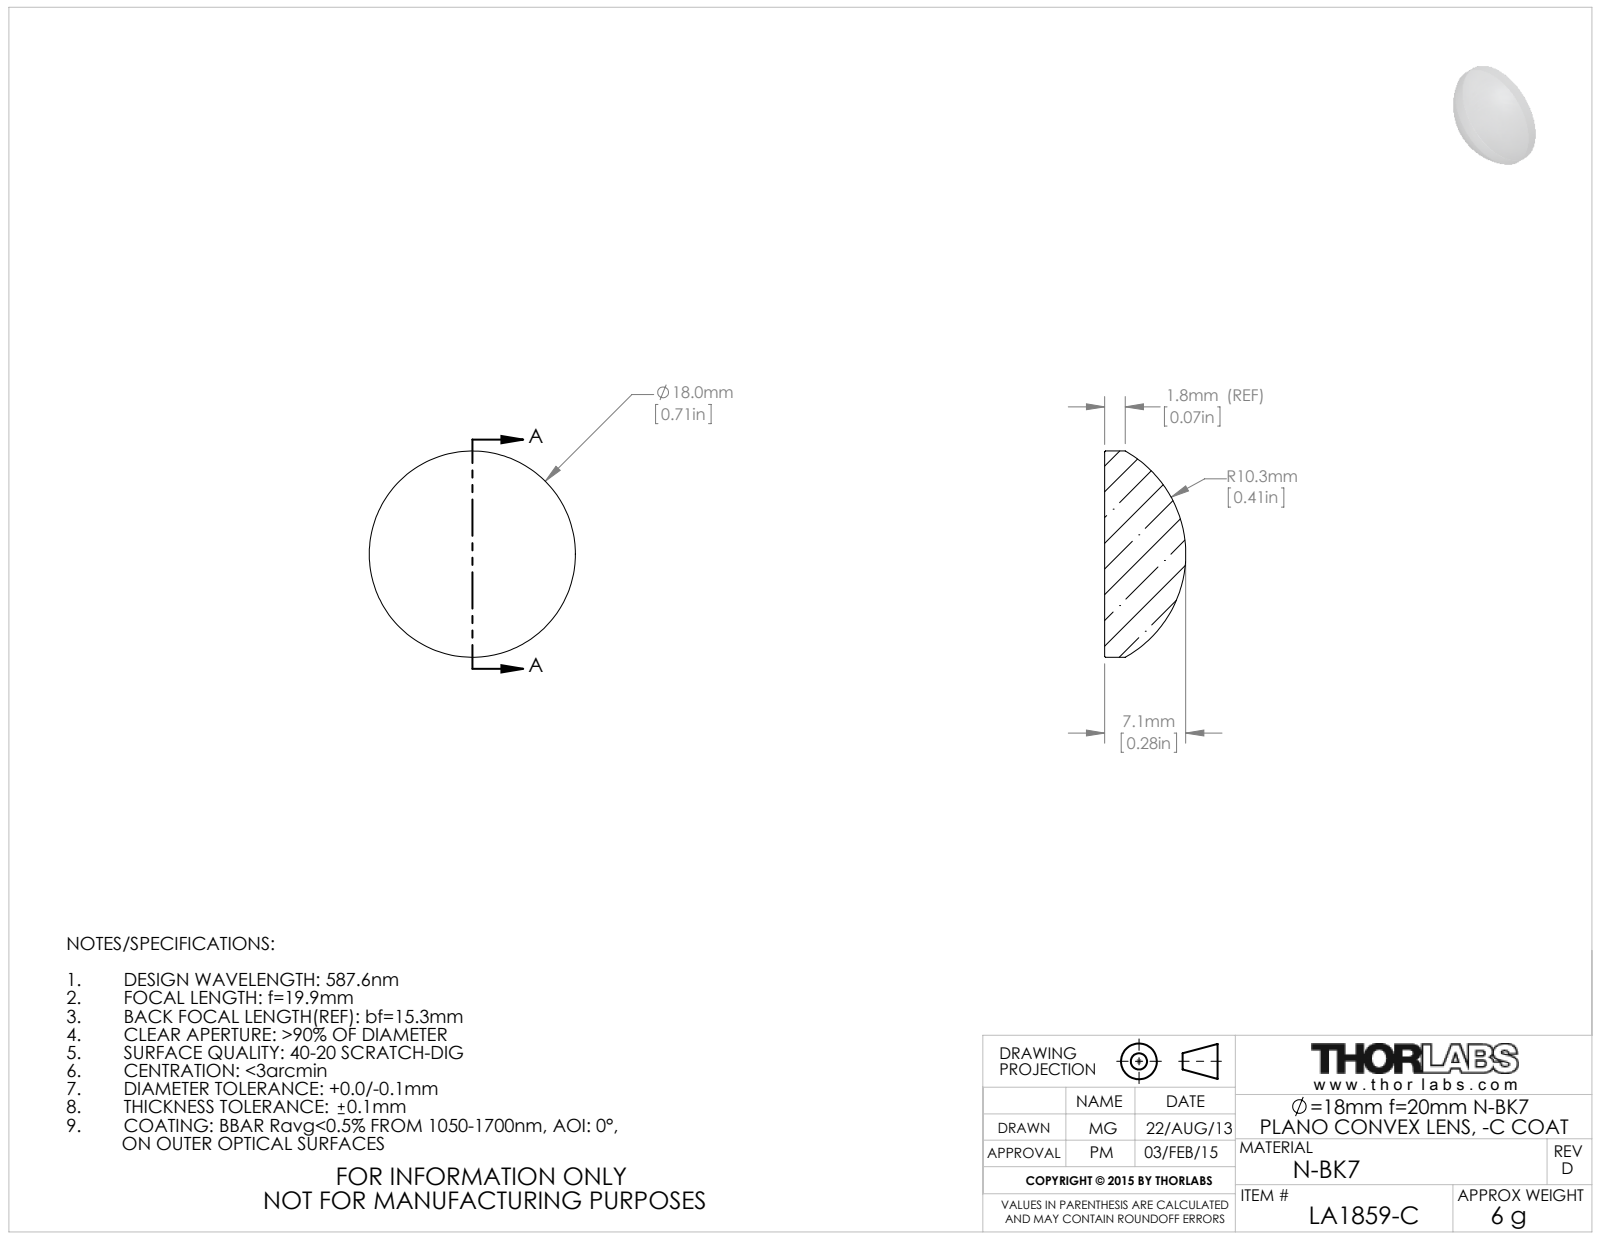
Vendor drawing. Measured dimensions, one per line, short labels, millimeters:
name: 4573-E0W
written by: SolidWorks 2009 (AUTOMOTIVE_DESIGN)
unit: mm
bodies: 1 solid, 5 faces (1 planar, 2 cylindrical, 2 other)
size: 18 × 18 × 7.08
volume: 1 206 mm³; area: 698 mm²
bosses: 1× ⌀18
